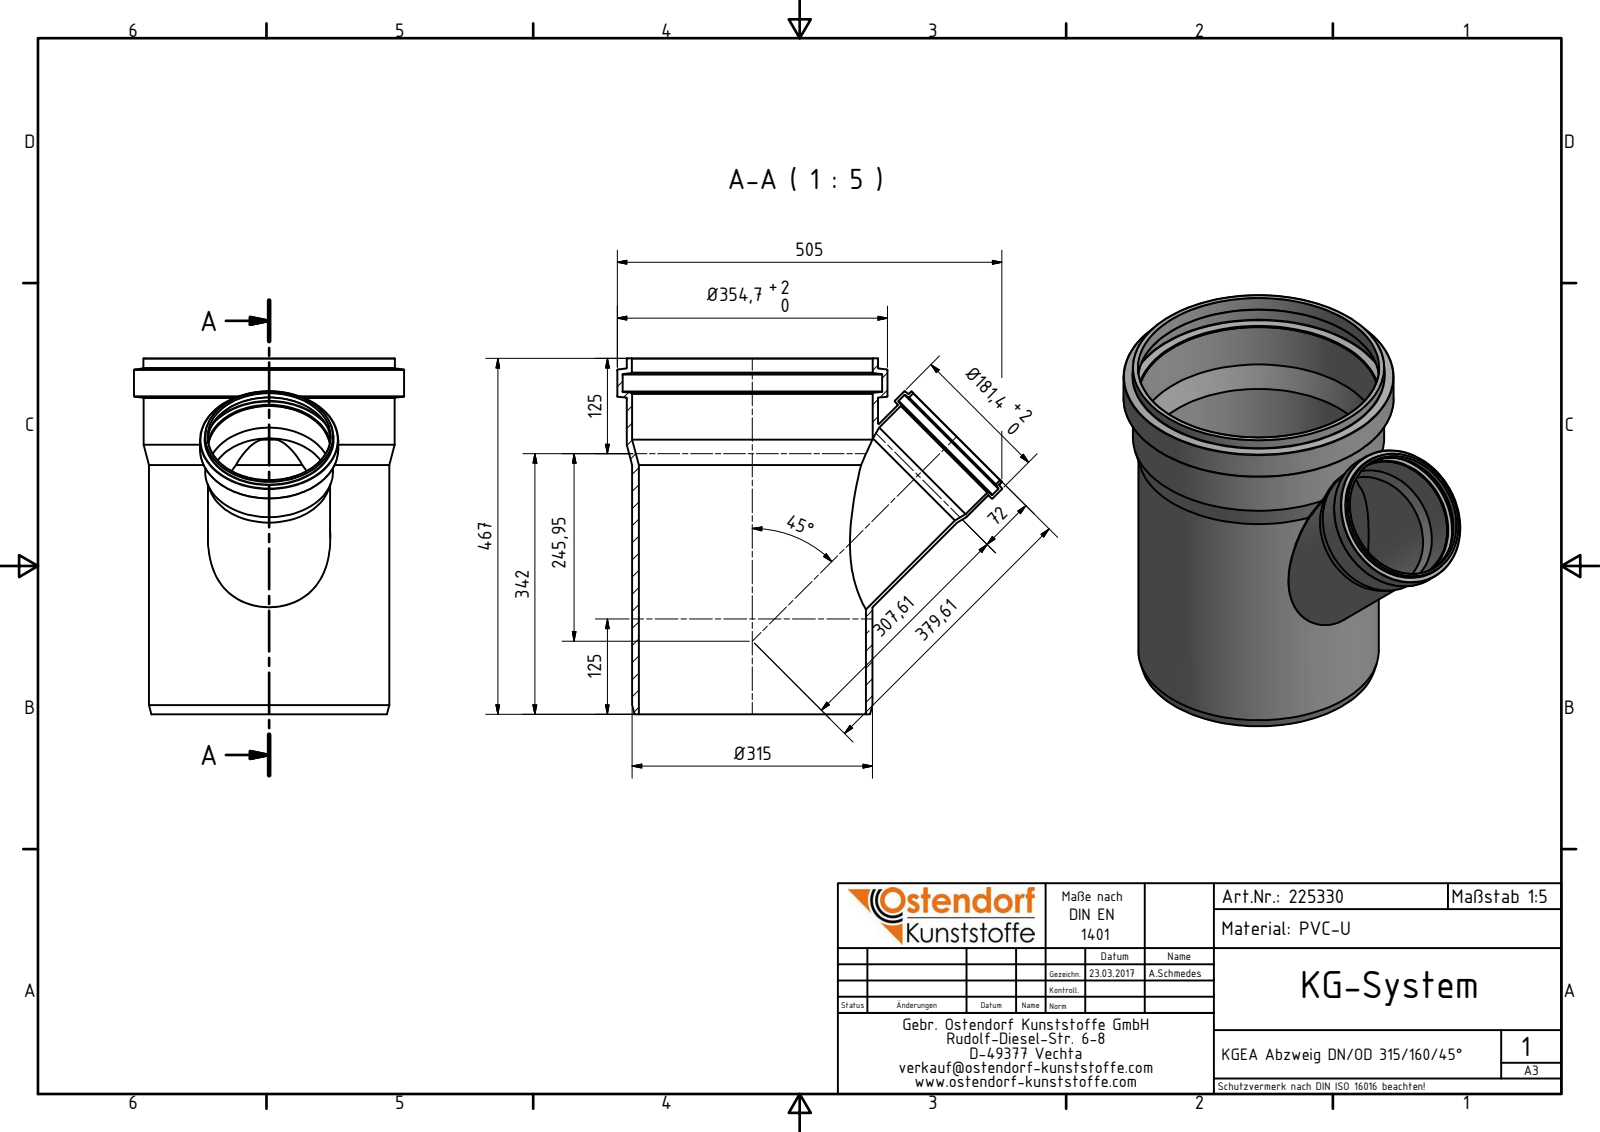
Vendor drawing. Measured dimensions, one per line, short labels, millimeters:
name: 225330 KGEA Abzweig DN_OD 315_160_45°
written by: Autodesk Inventor 2016 (AUTOMOTIVE_DESIGN)
unit: mm
bodies: 1 solid, 64 faces (5 planar, 18 cylindrical, 41 other)
size: 505.11 × 467 × 354.7
volume: 4 040 000 mm³; area: 1 109 000 mm²
holes: 2× ⌀161.1, 1× ⌀152.3, 1× ⌀160.7, 1× ⌀174.4, 1× ⌀298.2, 1× ⌀316, 1× ⌀316.3, 1× ⌀340.9
bosses: 1× ⌀354.7, 1× ⌀330.1, 1× ⌀329.8, 1× ⌀315.6, 1× ⌀181.4, 1× ⌀168.1, 1× ⌀167.7, 1× ⌀160.3
face distances: 467, 420.44, 46.56, 23.6
